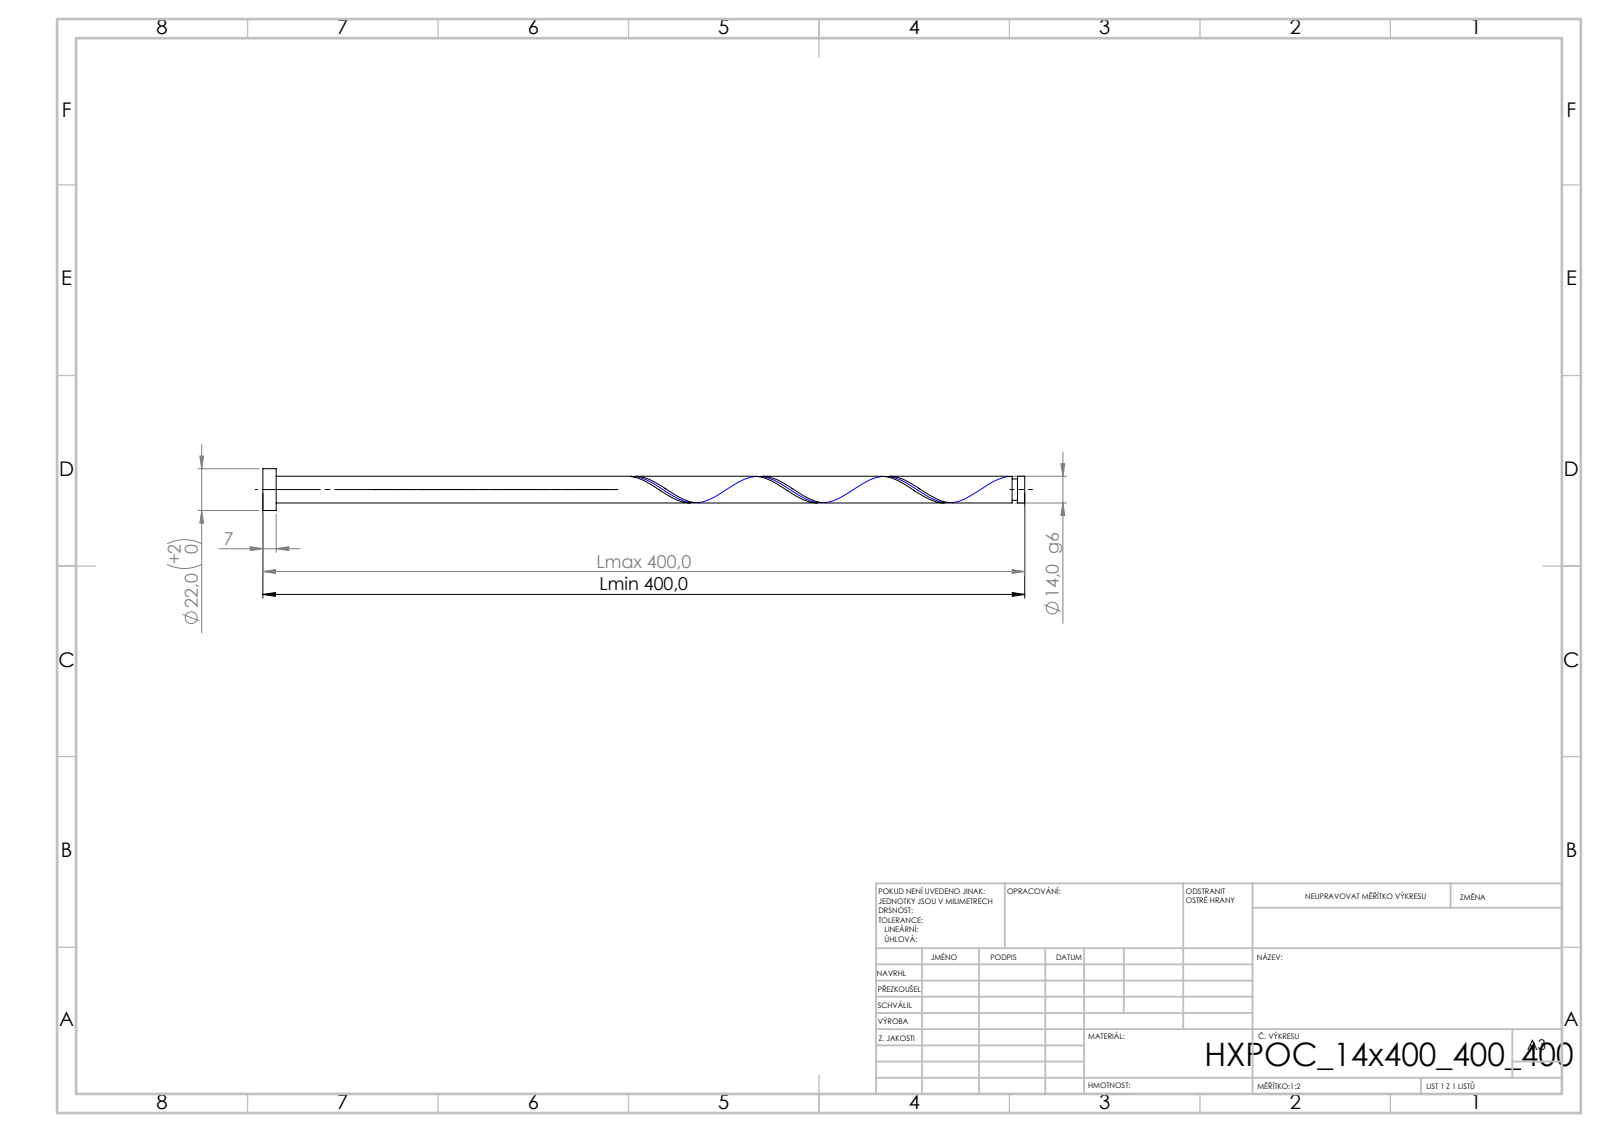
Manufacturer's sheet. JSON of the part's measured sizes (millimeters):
{"step_written_by": "SolidWorks 2019 (CONFIG_CONTROL_DESIGN)", "units": "millimeters", "bodies": {"solids": 1, "faces": 21, "planar": 6, "cylindrical": 14, "other": 1}, "overall_size": [400, 22, 22], "volume_mm3": 62414, "surface_area_mm2": 18956, "round_bosses_or_shafts": [[22, 1], [14, 1], [11.2, 1]], "face_to_face_distances": [7, 400, 393, 396.16, 389.16, 3.84, 393.36, 386.36, 2.8, 6.64]}
